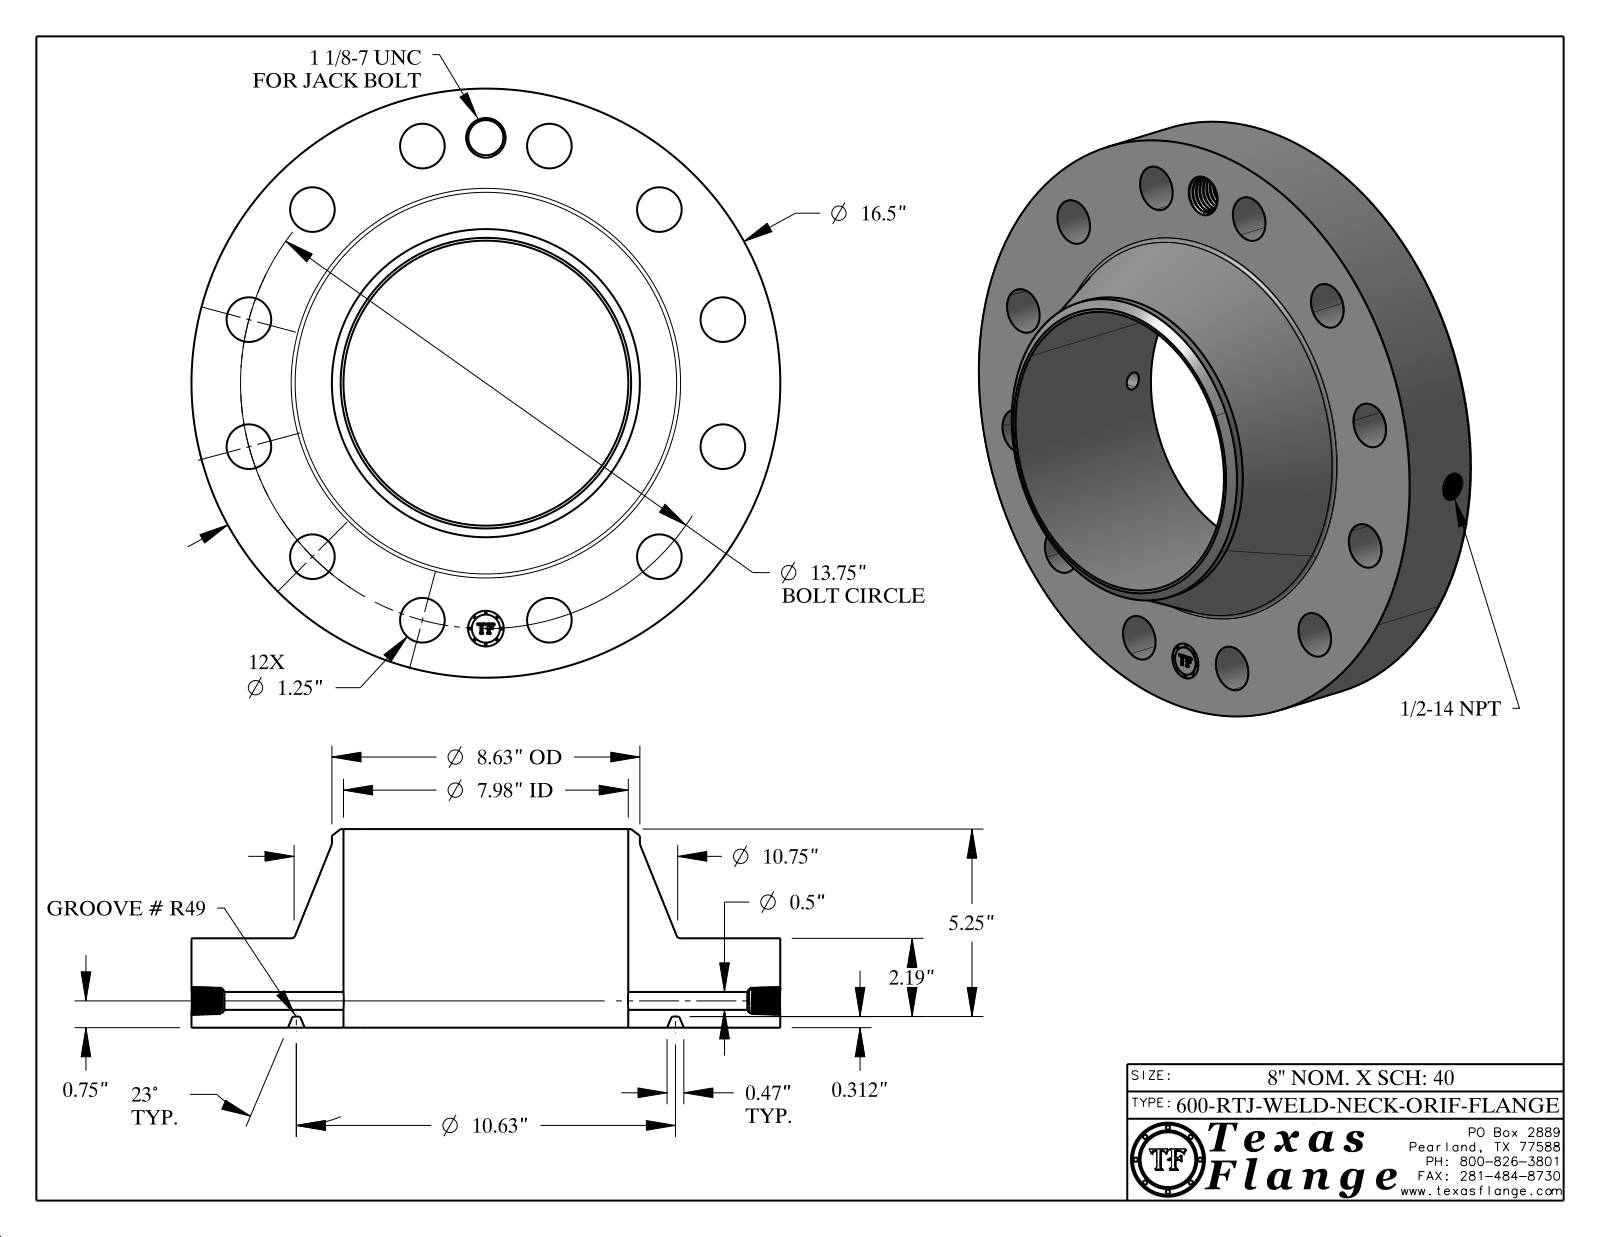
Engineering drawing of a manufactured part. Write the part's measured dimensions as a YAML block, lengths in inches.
part_name: "600-RTJ-WELD-NECK"
step_written_by: "CATIA V5 STEP AP214 (AUTOMOTIVE_DESIGN)"
units: inches
bodies: {solids: 1, faces: 801, planar: 370, cylindrical: 105, other: 326}
overall_size: [16.5, 16.5, 5.562]
volume: 431.5
surface_area: 787.1
round_holes:
  - {diameter: 1.25, count: 12}
  - {diameter: 0.5, count: 1}
  - {diameter: 0.672, count: 1}
  - {diameter: 0.984, count: 1}
  - {diameter: 1, count: 1}
  - {diameter: 7.981, count: 1}
round_bosses_or_shafts:
  - {diameter: 0.061, count: 8}
  - {diameter: 16.5, count: 1}
  - {diameter: 8.63, count: 1}
  - {diameter: 0.788, count: 1}
face_to_face_distances: [2.502, 0.312, 2.19, 5.562, 5.25, 3.06, 0.015, 2.487, 2.175, 3.075]
hole_center_spacings: [6.875, 11.908, 3.559, 6.875, 9.722, 13.281, 1.795, 3.559]
